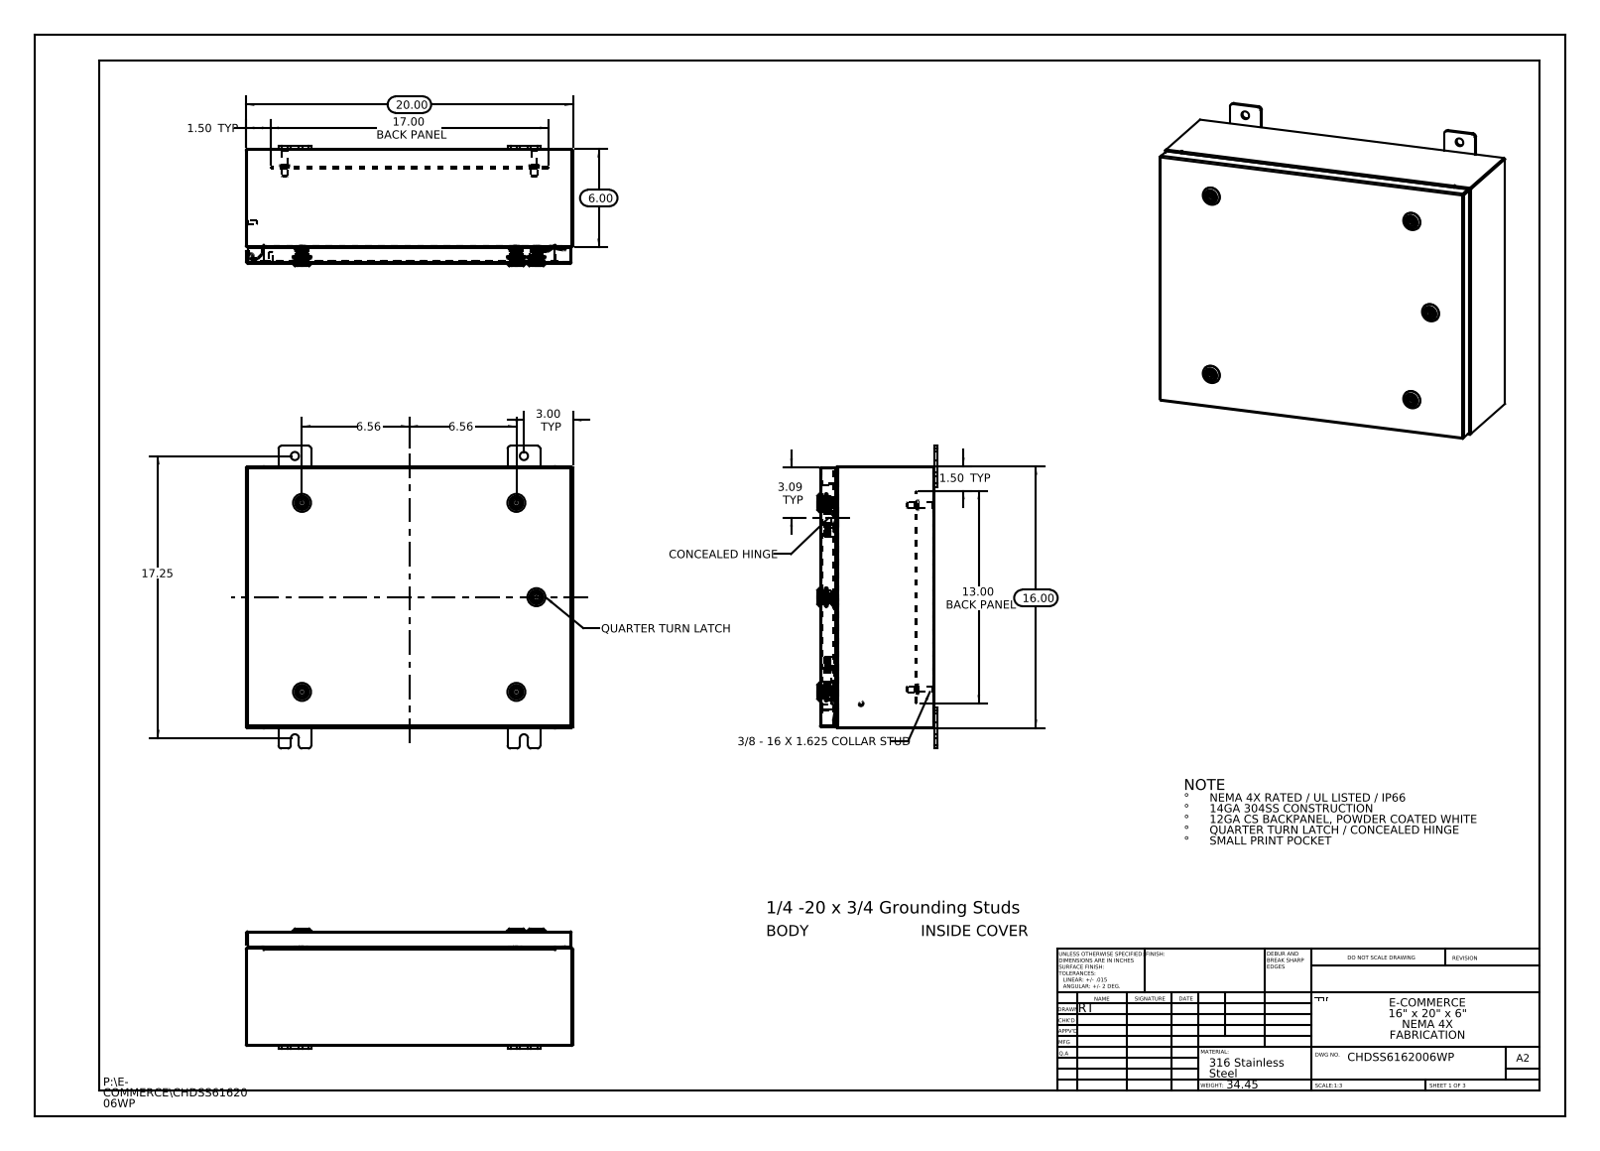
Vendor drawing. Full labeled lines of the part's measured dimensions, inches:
Part name (STEP PRODUCT): CHDSS6162006WP Mounting Studs; CHDSS6162006WP Bottom; CHDSS6162006WP Mounting Feet; CHDSS6162006WP (+8 more)
STEP written by: SolidWorks 2013 (CONFIG_CONTROL_DESIGN)
Units: inches
Bodies: 49 solids, 4592 faces (1366 planar, 1436 cylindrical, 1790 other)
Overall size (bounding box): 20 × 18.5 × 7.356
Volume: 124.2 in³ · Surface area: 3 114 in²
Round holes (diameter × count): ⌀0.5 ×8, ⌀0.197 ×5, ⌀0.394 ×5, ⌀0.4 ×5, ⌀0.63 ×5, ⌀0.787 ×5, ⌀0.136 ×4, ⌀0.211 ×1
Round bosses / shafts (diameter × count): ⌀0.236 ×7, ⌀1.102 ×5, ⌀0.78 ×5, ⌀0.626 ×5, ⌀0.61 ×5, ⌀0.531 ×5, ⌀0.392 ×5, ⌀0.114 ×5
Partial cylindrical surfaces — rounded edges, fillets, slot ends (radius × count): R0.006 ×165, R0.118 ×165, R0.028 ×60, R0.19 ×24, R0.02 ×20, R0.197 ×20, R0.013 ×18, R0.088 ×18
Main face-to-face distances: 0.075, 0.074, 7.01, 6.935, 6.936, 6.861, 15.925, 1, 1.075, 5.861
Hole centre spacings: 0.688, 1.858, 3.065, 5.627, 9.687, 11.25, 11.55, 13.015
